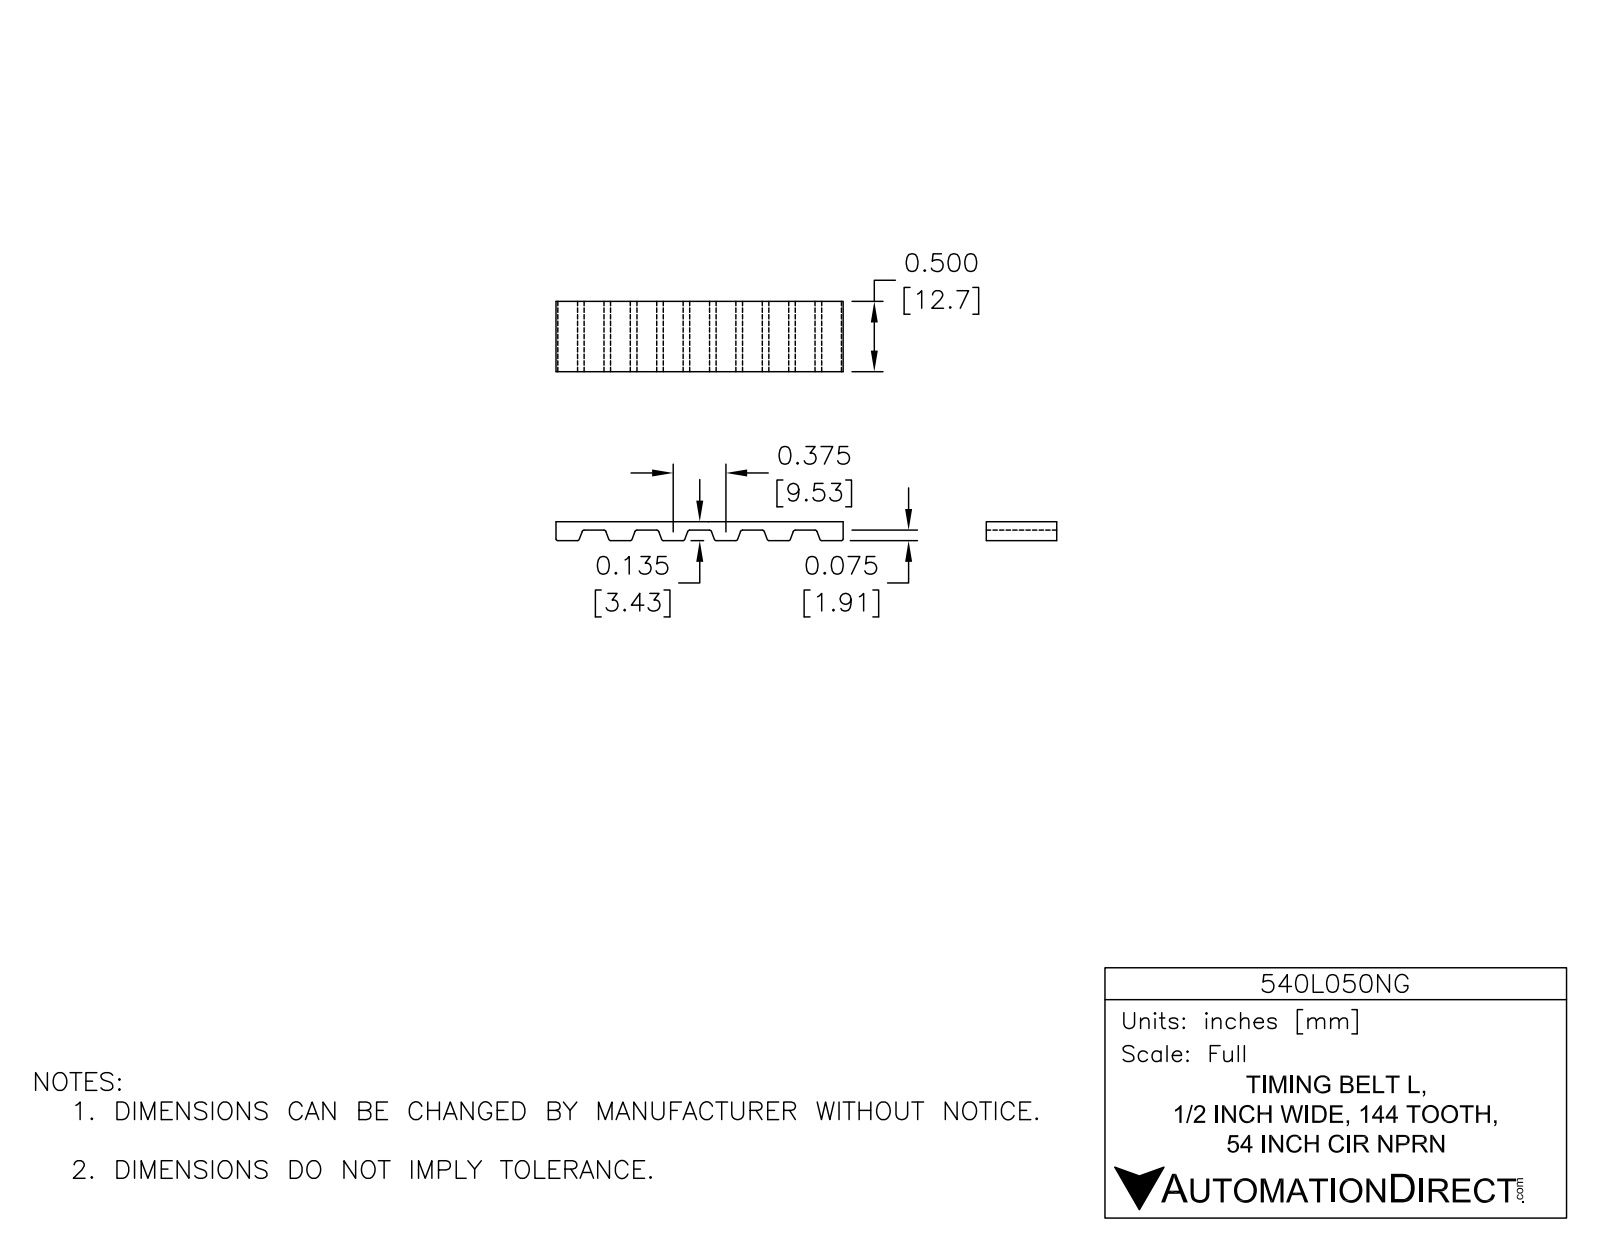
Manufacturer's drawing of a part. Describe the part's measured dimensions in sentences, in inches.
The part is named "540L050NG". Its 3-D file was written by "SolidWorks 2014 (AUTOMOTIVE_DESIGN)". It is 1 solid with 1168 faces: 553 planar, 615 cylindrical and 0 other. Overall it measures 25.288 by 3 by 0.5 inches. Its volume is 2.453 cubic inches and its surface area 70.09 square inches. Partial cylindrical surfaces (rounded edges, fillets, slot ends): 572 of radius 0.02, 2 of radius 1.435, 2 of radius 1.5. The main face-to-face distances are 0.065, 2.935, 3, 2.87, 0.5, 0.14, 2.86, 0.075, 2.795, 2.72.
